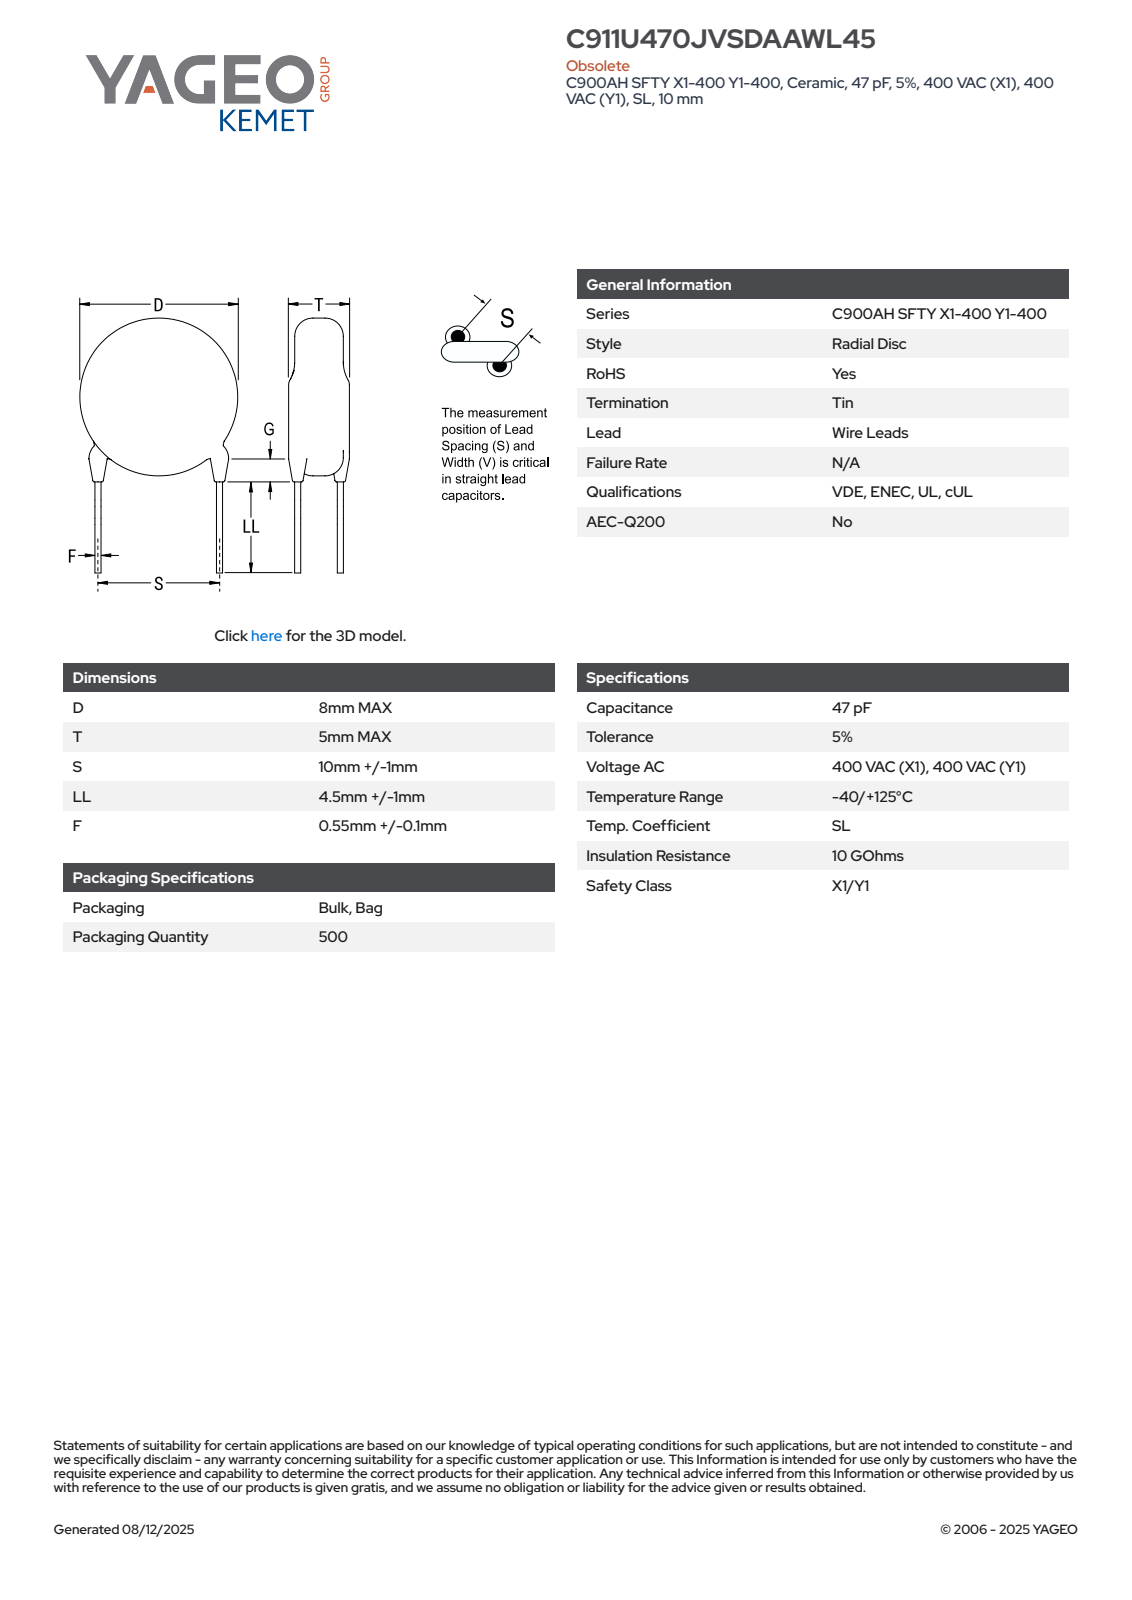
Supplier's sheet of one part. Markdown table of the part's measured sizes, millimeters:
| quantity | value |
| --- | --- |
| part name | CCD_STC900_D8T5S10LL5.5F0.65G3 |
| STEP written by | SolidWorks 2014 (AUTOMOTIVE_DESIGN) |
| units | millimeters |
| bodies | 4 solids, 83 faces (61 planar, 6 cylindrical, 16 other) |
| overall size | 13.92 × 10.19 × 5 |
| volume | 250 mm³ |
| surface area | 247 mm² |
| round bosses / shafts (diameter × count) | 0.65 × 2, 8 × 1 |
| main face-to-face distances | 5, 10.38, 9.46, 0.92, 0.4, 1.04, 3.77, 0.57, 2.73, 2.84 |
